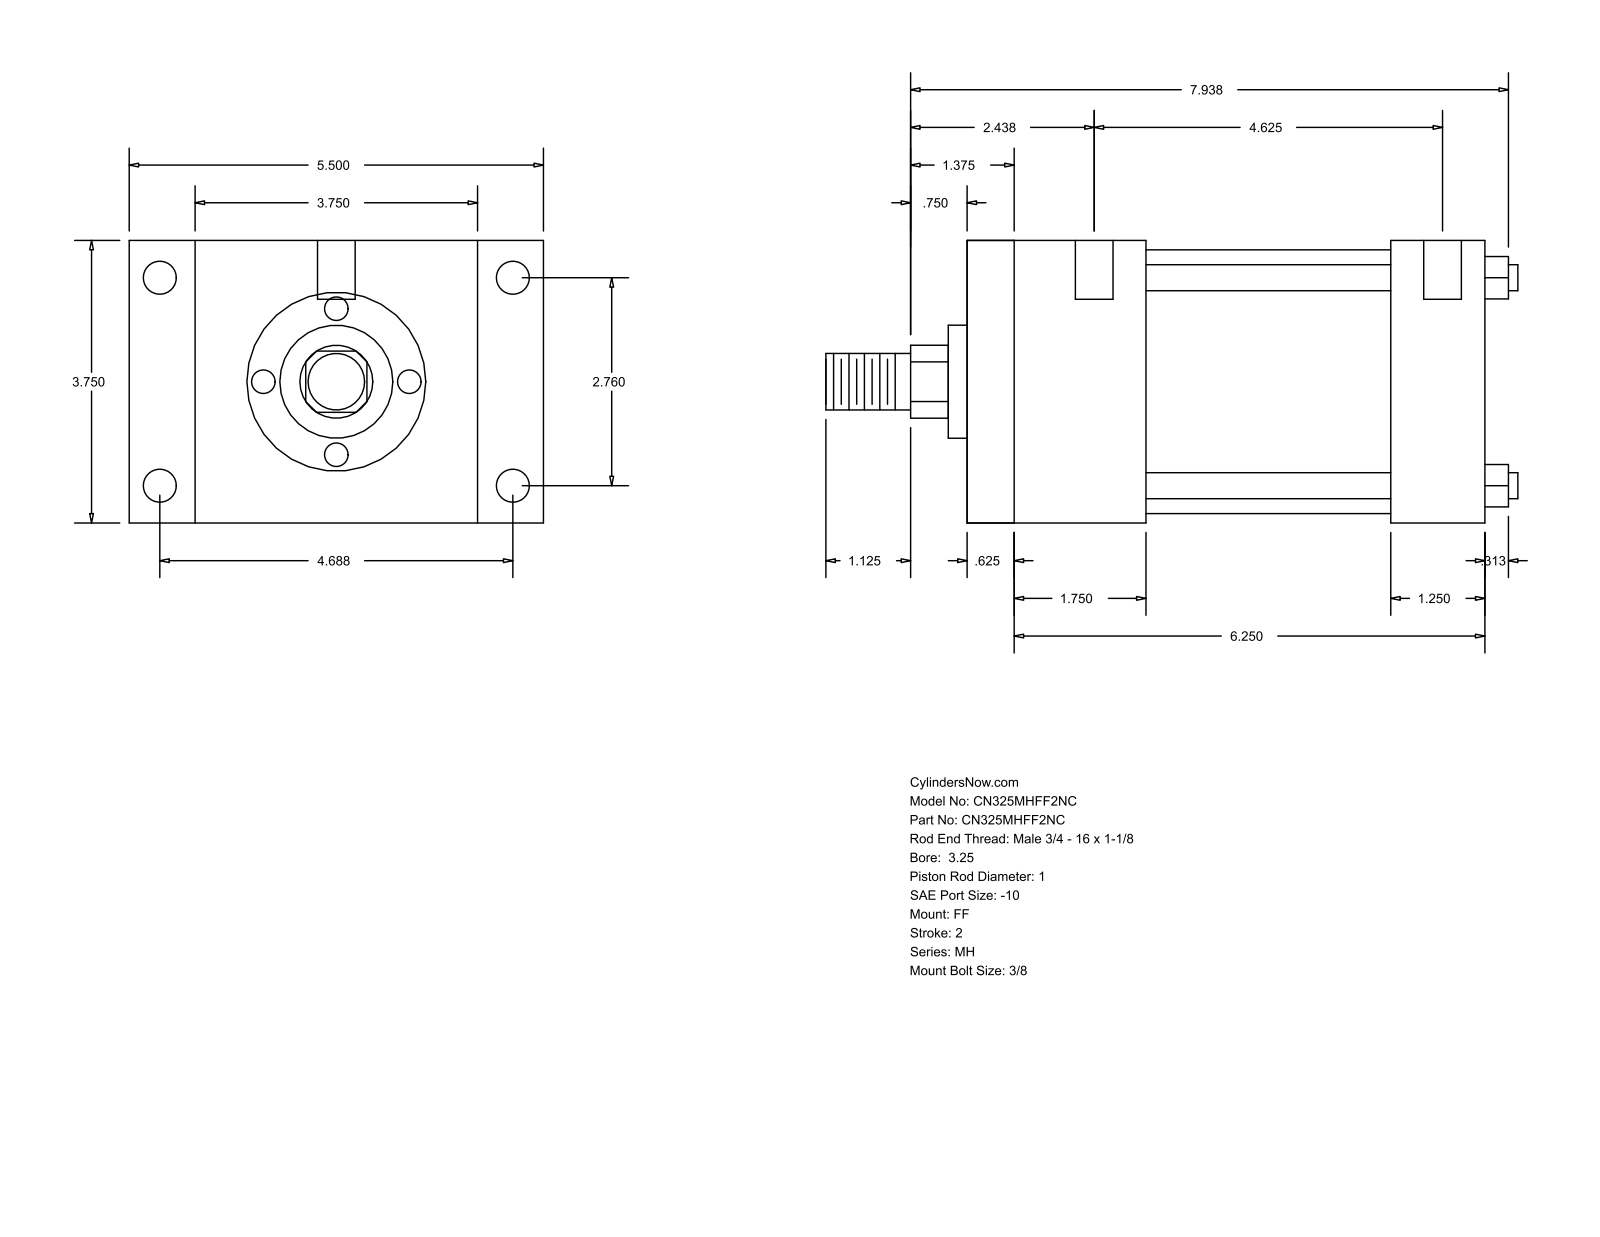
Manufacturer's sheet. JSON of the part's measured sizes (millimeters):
{"part_name": "MH_FF__0325_1", "step_written_by": "GSSL Pune (CONFIG_CONTROL_DESIGN)", "units": "millimeters", "bodies": {"solids": 0, "faces": 92, "planar": 64, "cylindrical": 28, "other": 0}, "overall_size": [233.36, 139.7, 95.25], "round_holes": [[5.56, 4], [11.13, 4], [12.7, 2]], "round_bosses_or_shafts": [[8.76, 4], [88.9, 1], [38.1, 1], [25.4, 1], [19.05, 1]], "partial_cylinders_radius": [[12.29, 1]], "face_to_face_distances": [95.24, 174.63, 15.87, 158.76, 22.23, 117.47, 142.88, 127.01, 31.75, 60.33], "hole_center_spacings": [119.06, 70.1, 123.82, 138.16, 1.58, 4.76, 117.48, 122.24]}
